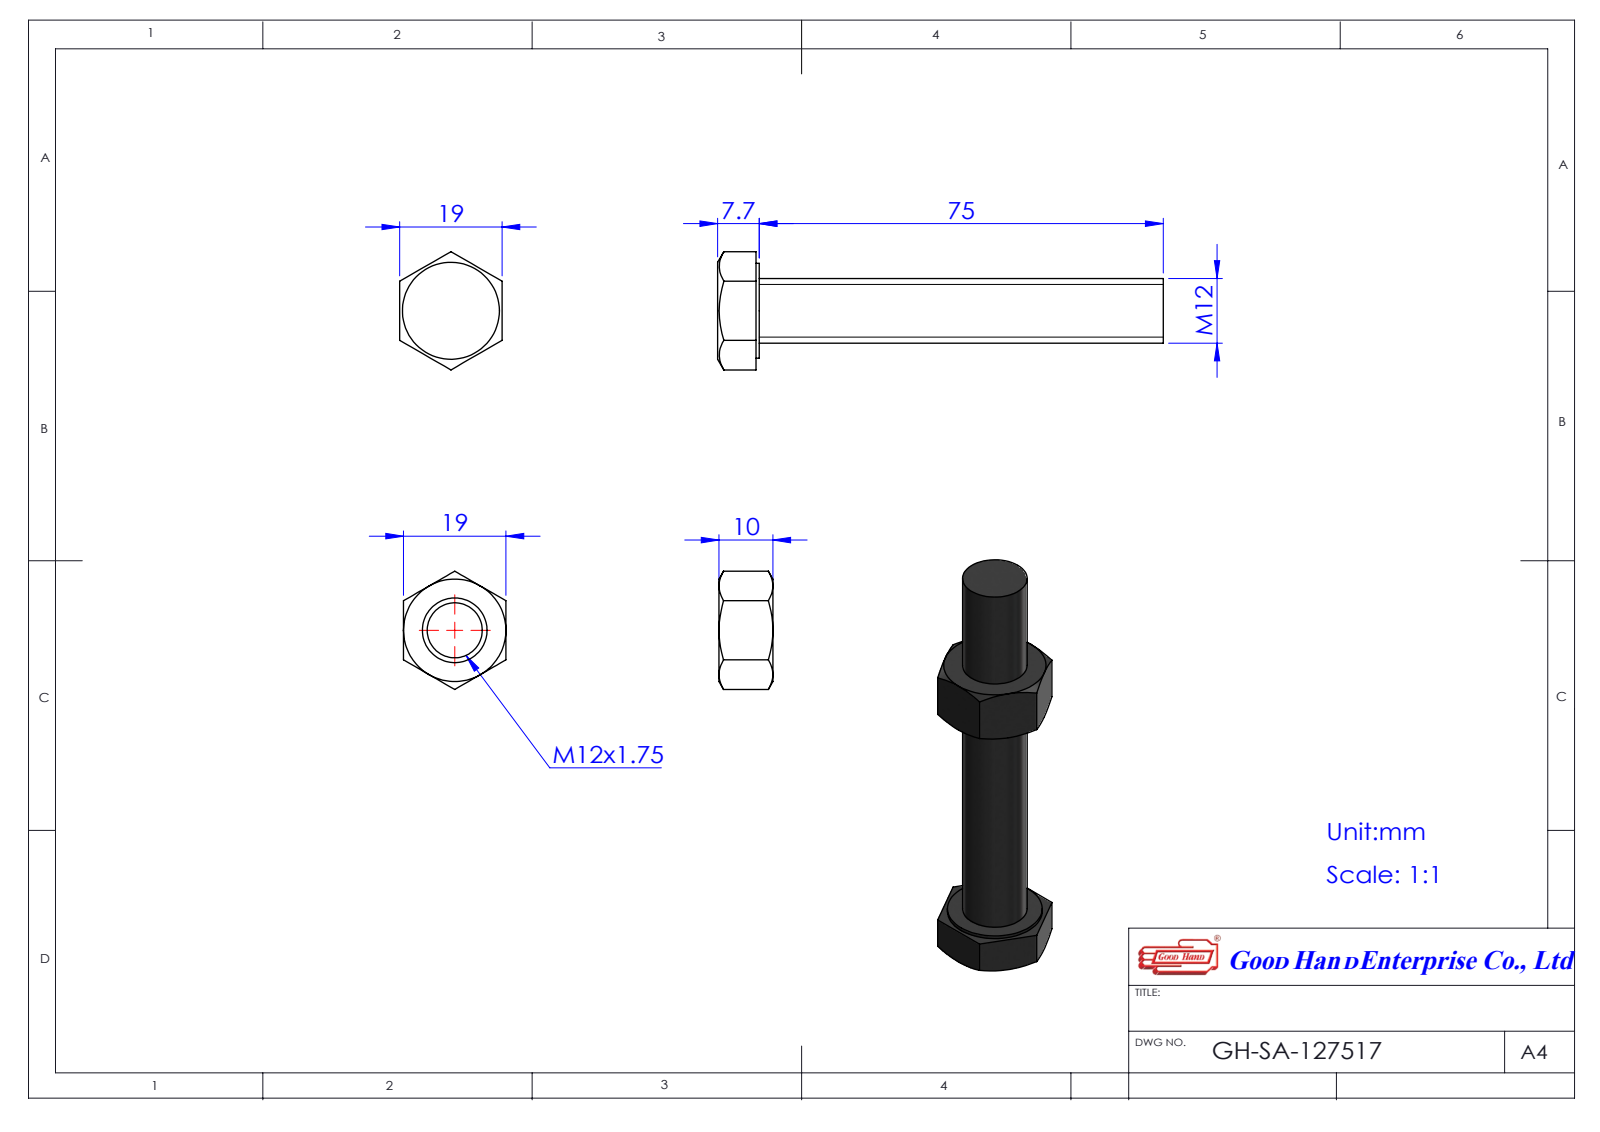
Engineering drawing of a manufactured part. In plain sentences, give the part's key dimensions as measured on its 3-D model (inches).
The part is named "6200120K(DIN934_JIS_)_JIS B 1181 Hexagon nut - Class 2 Finished M12 --N; SA-127517". Its 3-D file was written by "SolidWorks 2016 (AUTOMOTIVE_DESIGN)". It is 2 solids with 44 faces: 18 planar, 8 cylindrical and 18 other. Overall it measures 3.256 by 0.864 by 0.748 inches. Its volume is 0.8 cubic inches and its surface area 8.229 square inches. Round holes: 1 of diameter 0.402, 1 of diameter 0.472. Round bosses or shafts: 1 of diameter 0.693. The main face-to-face distances are 0.748, 2.479, 2.085, 0.394, 0.303, 1.782, 2.176, 3.256, 2.953, 1.17.
